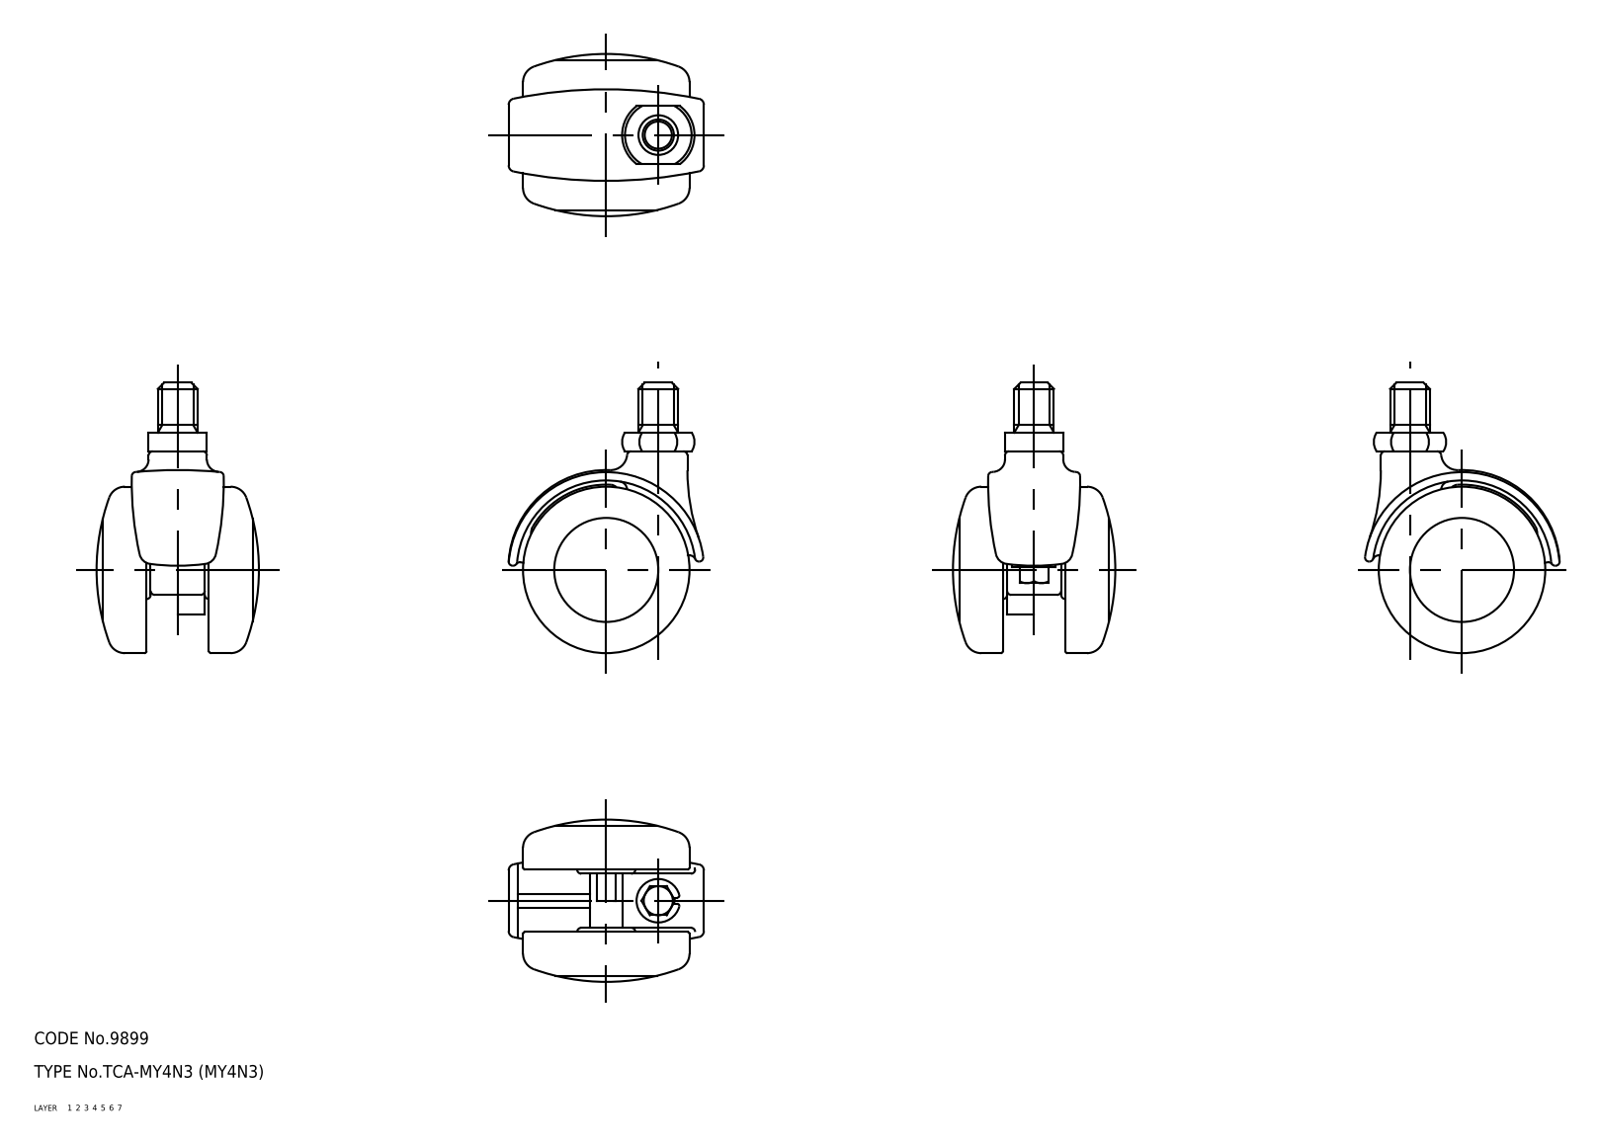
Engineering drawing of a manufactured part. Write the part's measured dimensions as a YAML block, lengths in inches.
part_name: "wheel; main shaft; MY4N3_14572_36"
step_written_by: "CADfix (AUTOMOTIVE_DESIGN)"
units: inches
bodies: {solids: 5, faces: 166, planar: 0, cylindrical: 0, other: 166}
overall_size: [2.559, 1.879, 1.535]
volume: 1.869
surface_area: 28.9
